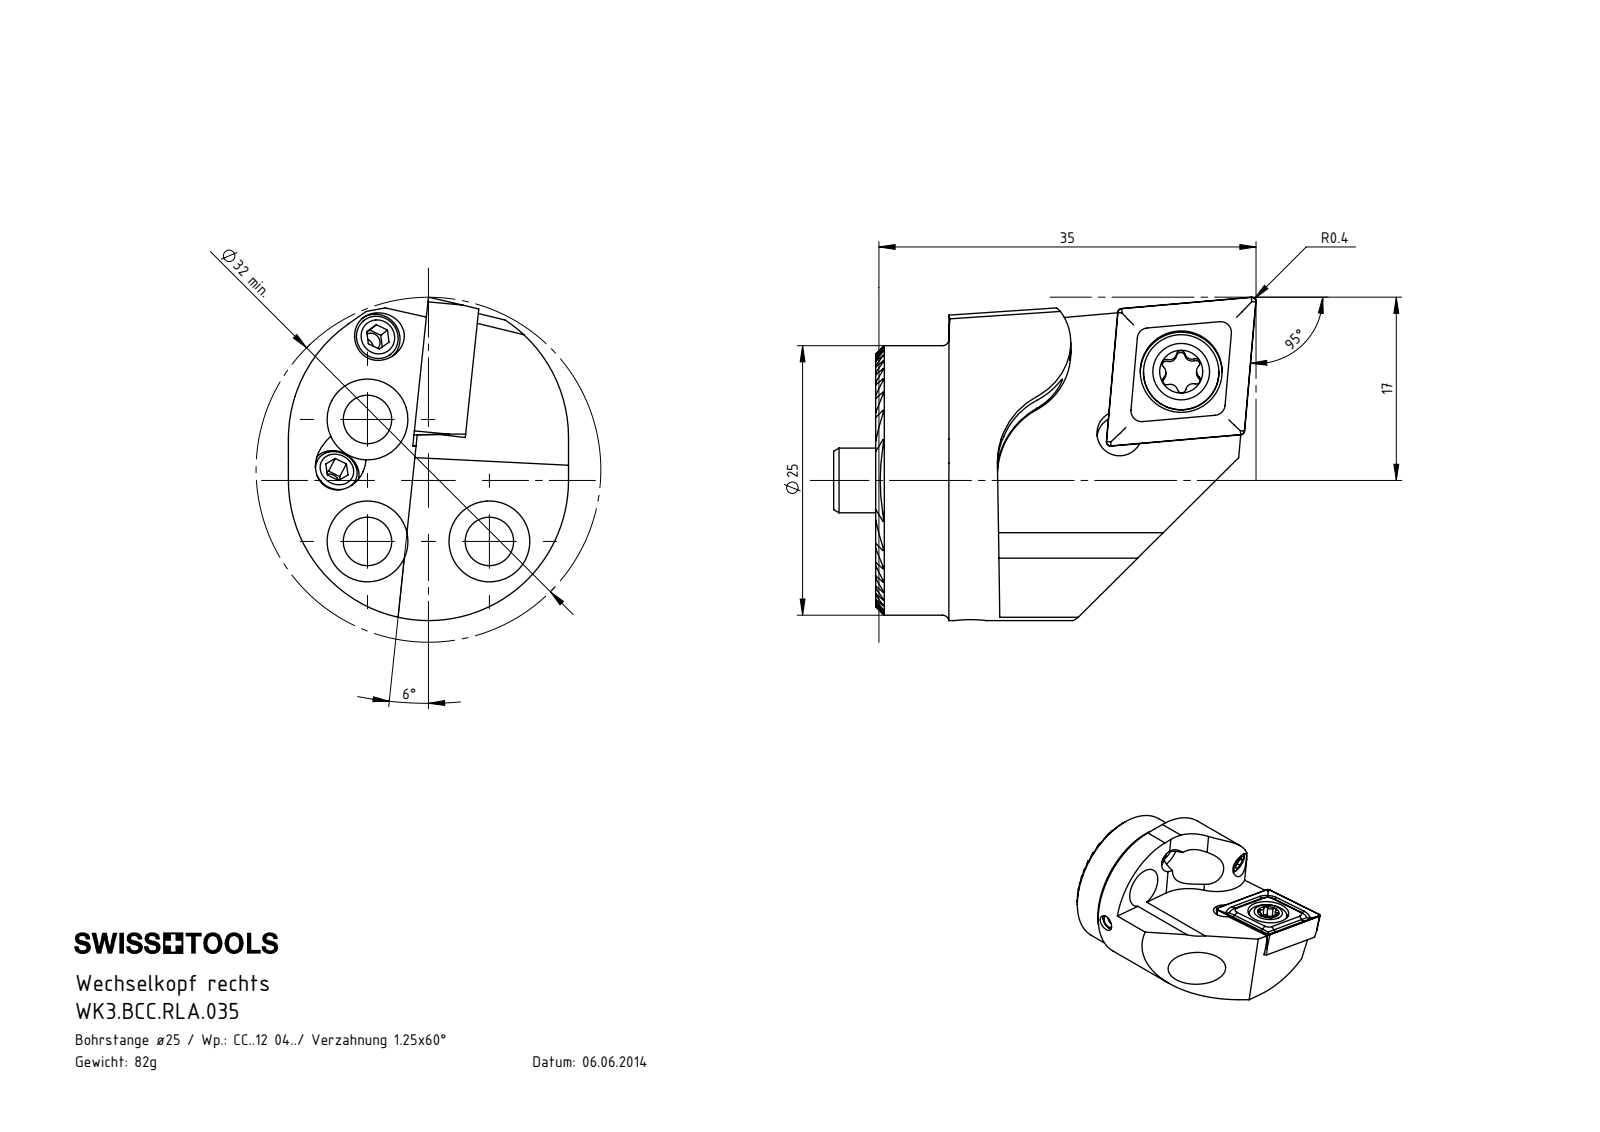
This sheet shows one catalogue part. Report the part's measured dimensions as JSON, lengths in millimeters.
{"part_name": "WK3-BCC.RLA.035_A; CCMT120404; KVT_MB_600_030; WKX-ER1.004.005_A_PreviewCfg (+3 more)", "step_written_by": "SolidWorks 2017 (AUTOMOTIVE_DESIGN)", "units": "millimeters", "bodies": {"solids": 12, "faces": 520, "planar": 177, "cylindrical": 174, "other": 169}, "overall_size": [39.2, 30, 26], "volume_mm3": 10483, "surface_area_mm2": 6961, "round_holes": [[4.5, 5], [2.38, 3], [2.5, 3], [4.2, 3], [7.5, 3], [1.7, 2], [3, 2], [3.3, 2], [5.5, 1], [6, 1], [7.6, 1]], "round_bosses_or_shafts": [[3, 3], [4, 2], [25, 1], [7, 1], [5, 1]], "partial_cylinders_radius": [[0.12, 20], [0.39, 6], [0.69, 3], [0.69, 3], [13, 3], [6, 1], [7, 1]], "face_to_face_distances": [4.33, 1.08, 3.25, 5.41, 4.45, 8.66, 7.58, 2.16, 2.17, 9.74], "hole_center_spacings": [8, 11.32, 8.08, 8.09, 16.01]}
